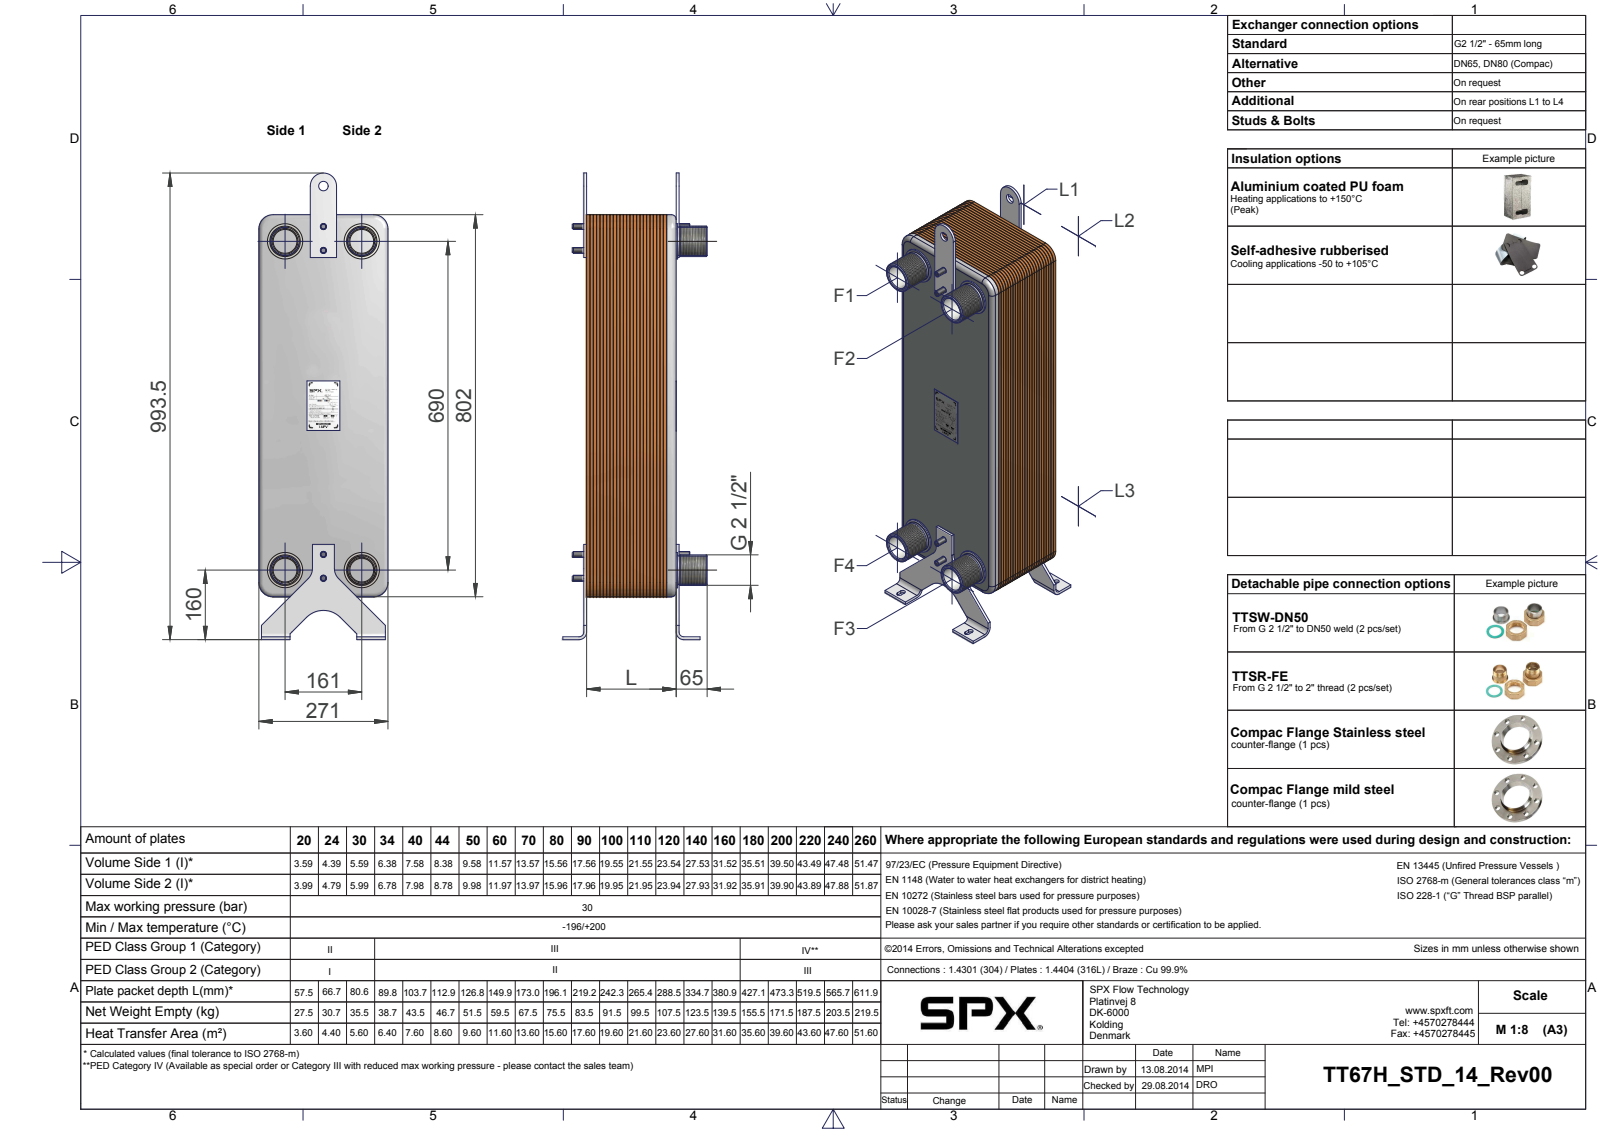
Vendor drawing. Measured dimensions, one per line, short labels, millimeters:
name: Platte mit Anschl\S\|ssen; Grundplatte; Kupferplatte; Kupferplatte_CPY (+8 more)
written by: Autodesk Inventor 2012 (AUTOMOTIVE_DESIGN)
unit: mm
bodies: 42 solids, 666 faces (344 planar, 186 cylindrical, 136 other)
size: 979.5 × 303 × 271
volume: 41 430 000 mm³; area: 11 520 000 mm²
holes: 4× ⌀13, 4× ⌀50, 1× ⌀20
bosses: 4× ⌀74, 4× ⌀64, 4× ⌀12, 4× ⌀9.85
rounds: 8× R5.5, 6× R10, 6× R30, 2× R16, 1× R27.5, 1× R50
face distances: 7, 14, 21, 42, 35, 28, 56, 49, 63, 70
hole spacings: 50, 82.28, 82.71, 86.26, 87, 141.2, 161, 661.91
